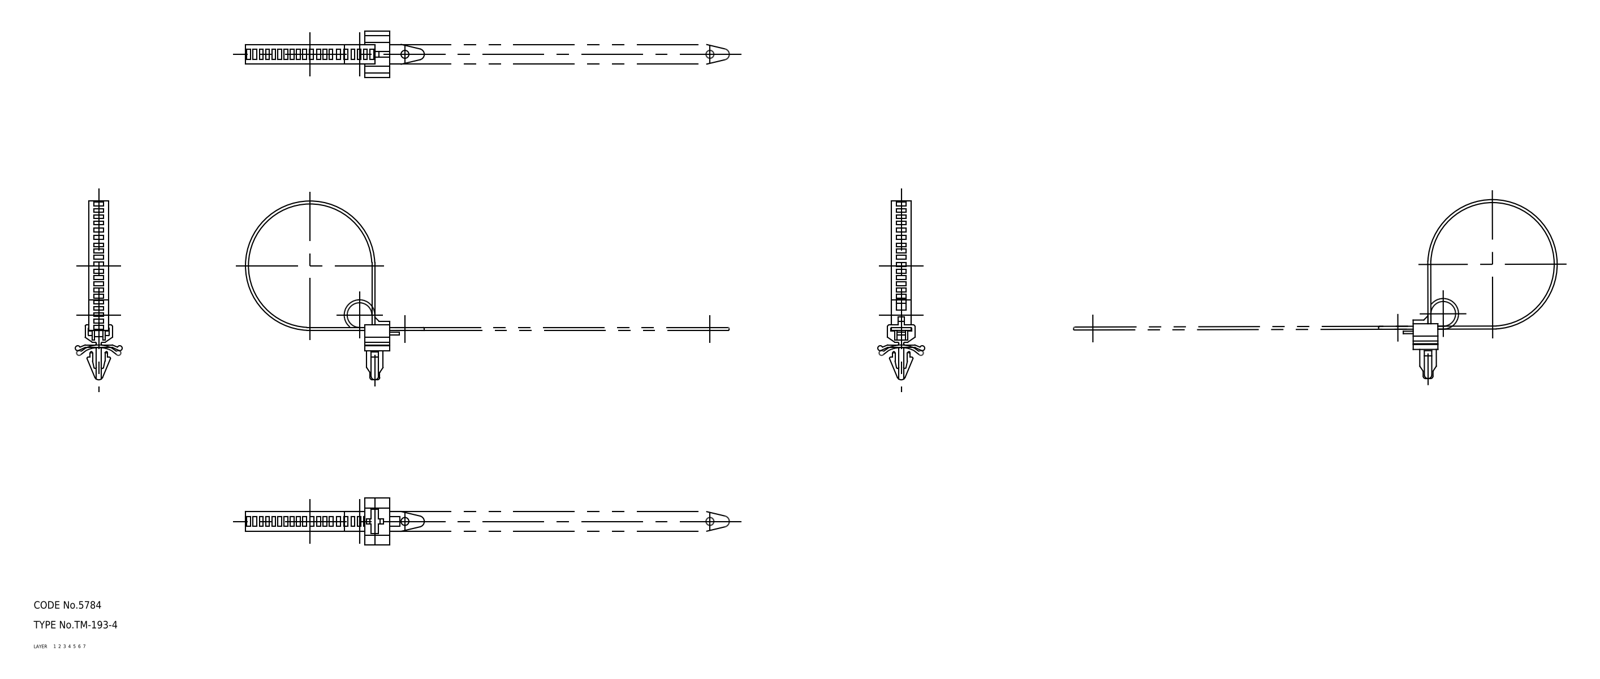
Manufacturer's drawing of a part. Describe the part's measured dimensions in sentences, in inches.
The part is named "clip". Its 3-D file was written by "CADfix (AUTOMOTIVE_DESIGN)". It is 1 solid with 201 faces: 0 planar, 0 cylindrical and 201 other. Overall it measures 2.85 by 2.85 by 0.748 inches. Its volume is 0.162 cubic inches and its surface area 7.654 square inches.
